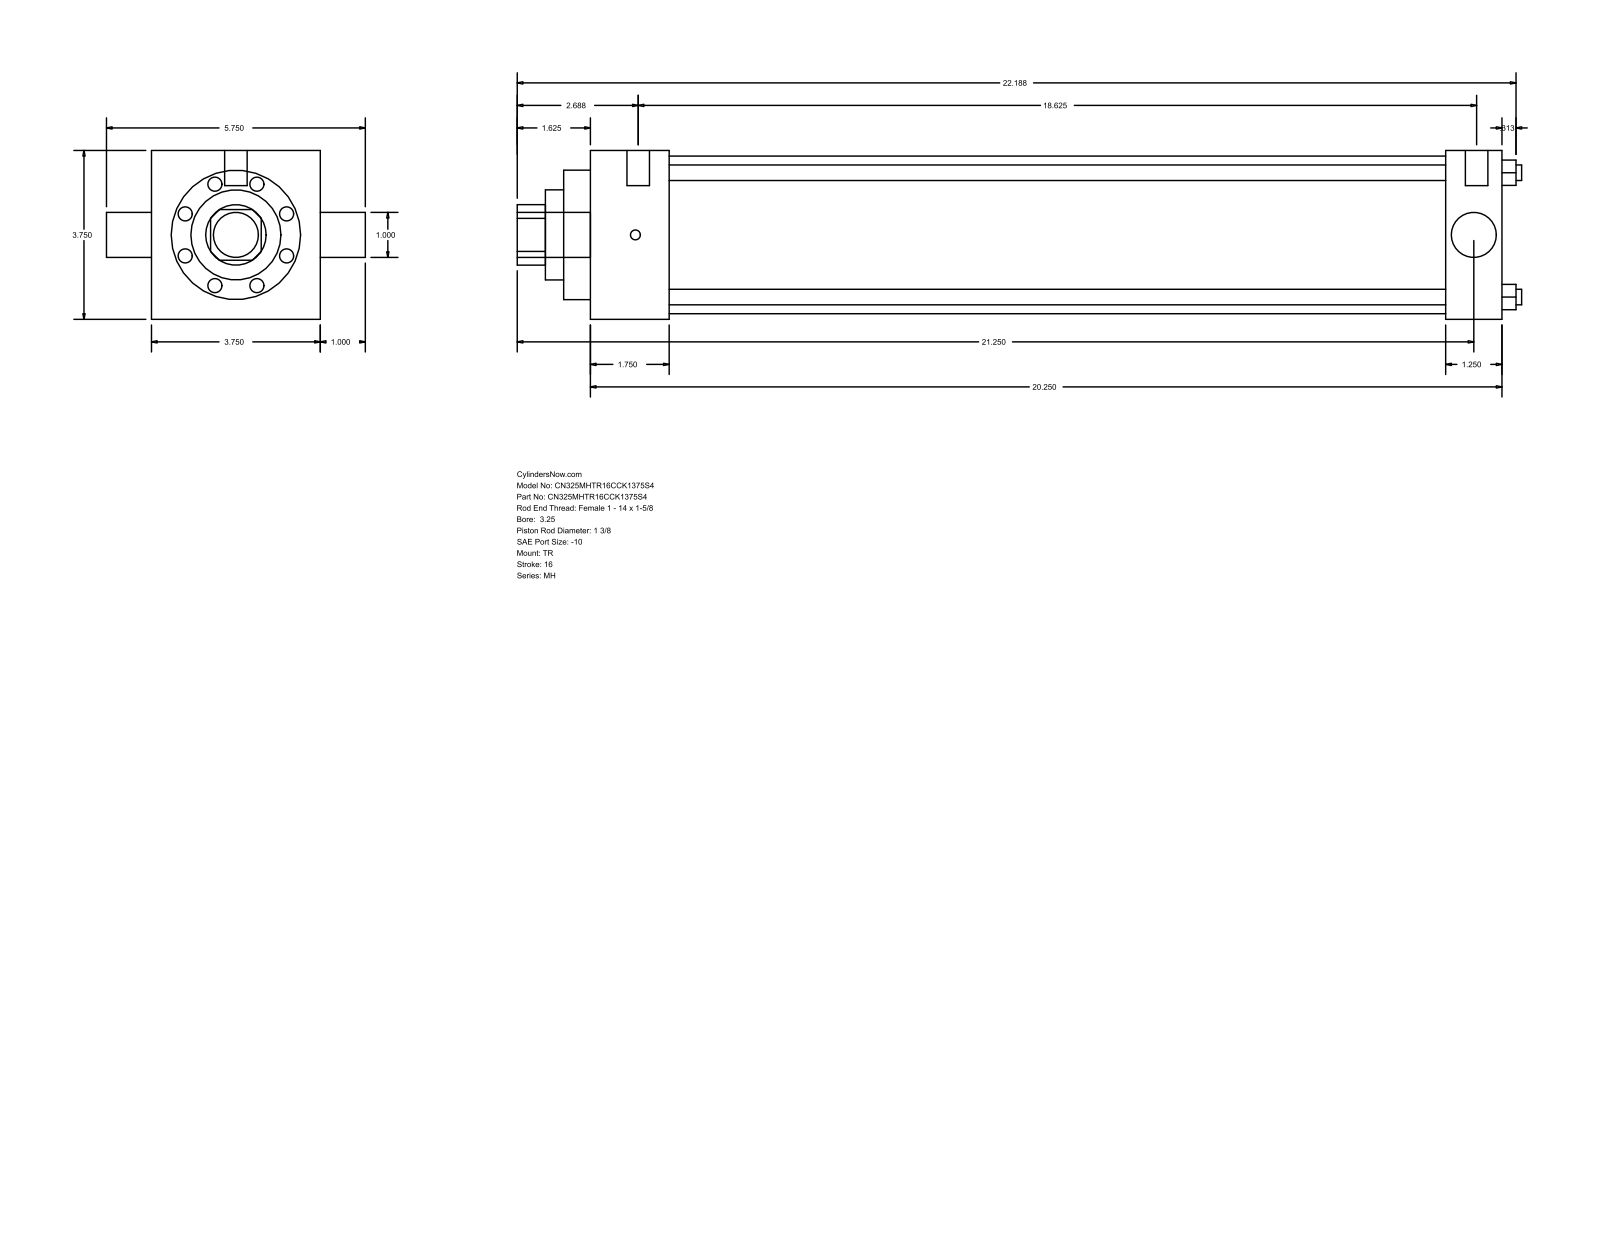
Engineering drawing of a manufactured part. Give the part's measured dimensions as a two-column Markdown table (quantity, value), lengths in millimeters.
| quantity | value |
| --- | --- |
| part name | MH_TR__0325_1.375 |
| STEP written by | GSSL Pune (CONFIG_CONTROL_DESIGN) |
| units | millimeters |
| bodies | 0 solids, 86 faces (61 planar, 25 cylindrical, 0 other) |
| overall size | 566.74 × 146.05 × 95.25 |
| round holes (diameter × count) | 8.76 × 4, 25.4 × 1, 34.92 × 1, 50.8 × 1, 73.03 × 1, 88.9 × 1 |
| round bosses / shafts (diameter × count) | 5.56 × 3, 12.7 × 2, 25.4 × 1 |
| partial cylindrical surfaces (radius × count) | 17.06 × 1 |
| main face-to-face distances | 95.24, 514.35, 44.45, 482.61, 438.16, 469.9, 31.74, 15.08, 59.53, 497.69 |
| hole center spacings | 49.57, 70.1, 99.14 |
